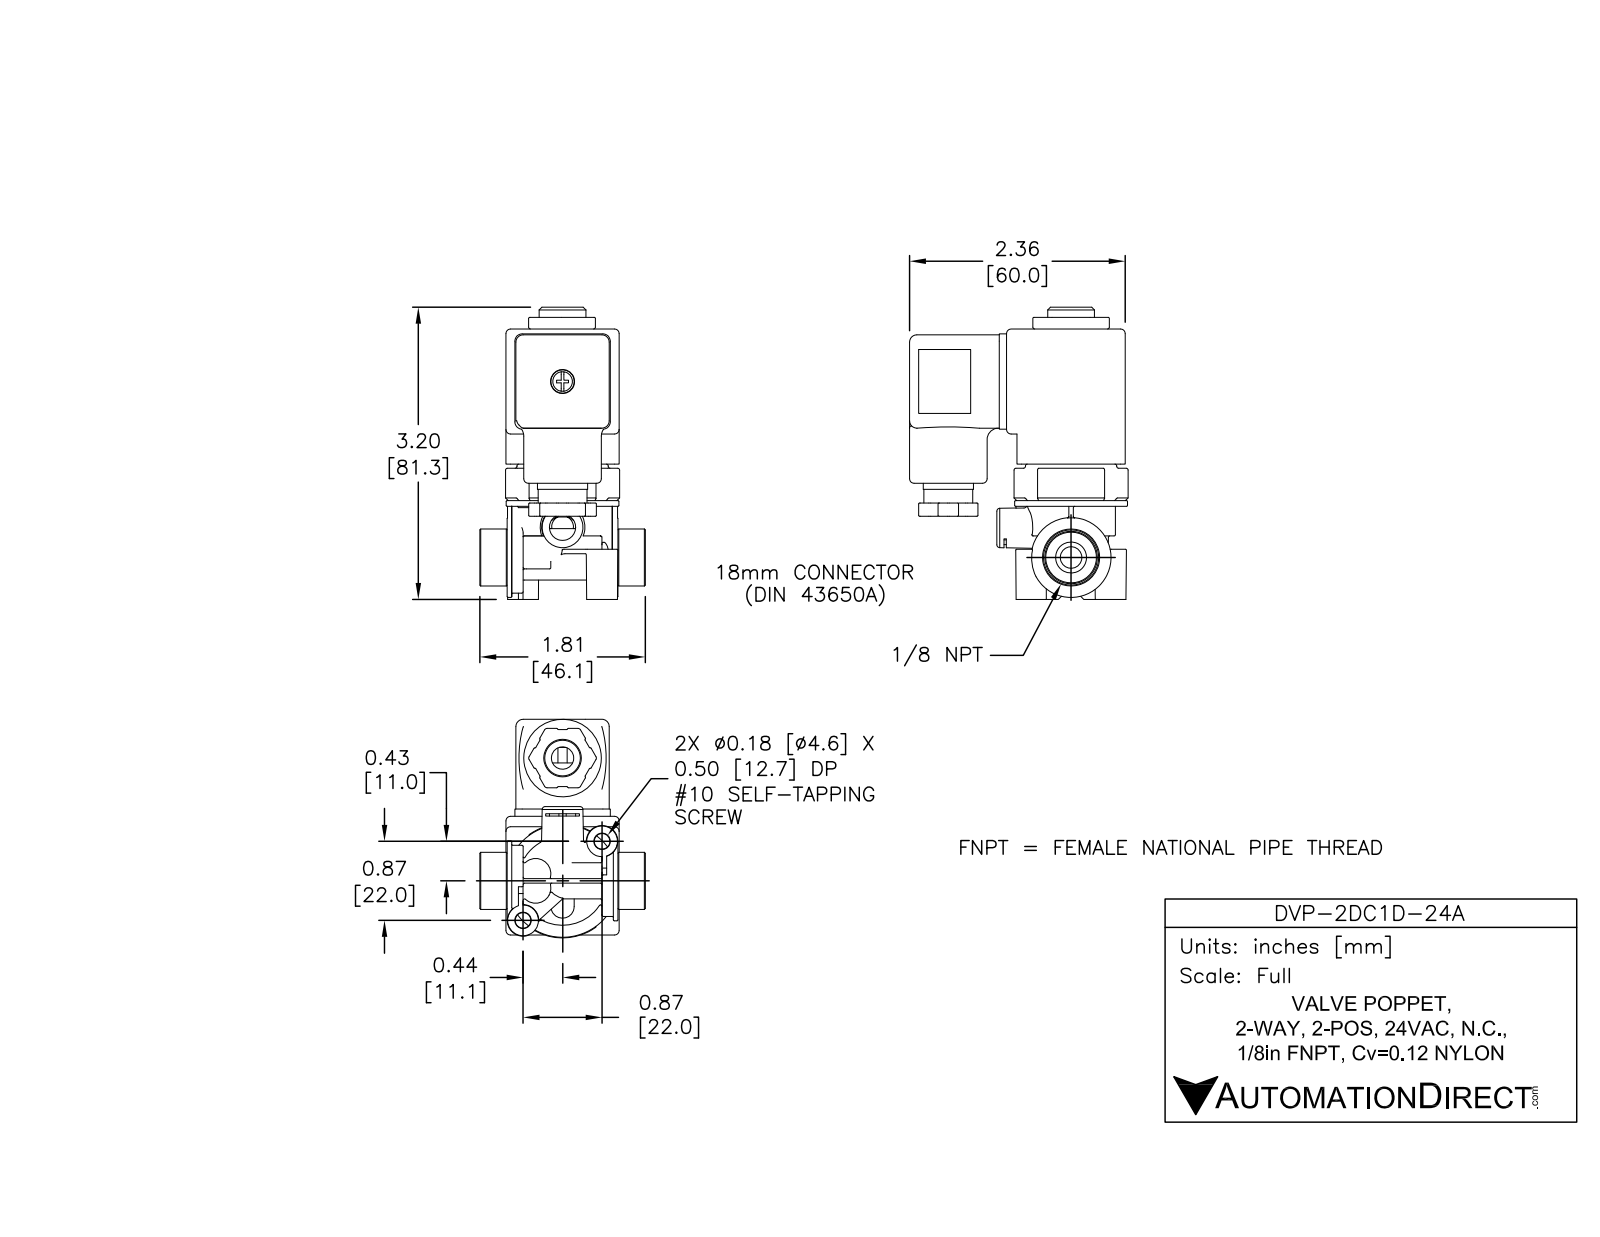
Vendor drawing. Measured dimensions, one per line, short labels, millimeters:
name: DVP-2DC1D-24A
written by: SolidWorks 2015 (AUTOMOTIVE_DESIGN)
unit: mm
bodies: 9 solids, 2037 faces (819 planar, 388 cylindrical, 830 other)
size: 81.7 × 60.8 × 46.1
volume: 66 250 mm³; area: 36 730 mm²
holes: 2× ⌀1.5, 2× ⌀6, 1× ⌀2, 1× ⌀2.6, 1× ⌀3, 1× ⌀5.2, 1× ⌀6.2, 1× ⌀6.7, 1× ⌀7.3, 1× ⌀8.6, 1× ⌀9.4, 1× ⌀9.5
bosses: 2× ⌀7.4, 1× ⌀31.4, 1× ⌀25.4, 1× ⌀24.7, 1× ⌀23.4, 1× ⌀22.6, 1× ⌀22.2, 1× ⌀21.6
rounds: 85× R0.3, 50× R0.4, 21× R1.3, 12× R0.5, 12× R2, 6× R0.7, 6× R0.8, 4× R1
face distances: 27.5, 31.5, 1.2, 4, 23.5, 37.6, 2.8, 28.7, 24.7, 34.7
hole spacings: 7.1, 7.2, 27, 34.1, 34.2, 40.9, 41.3, 55.5
